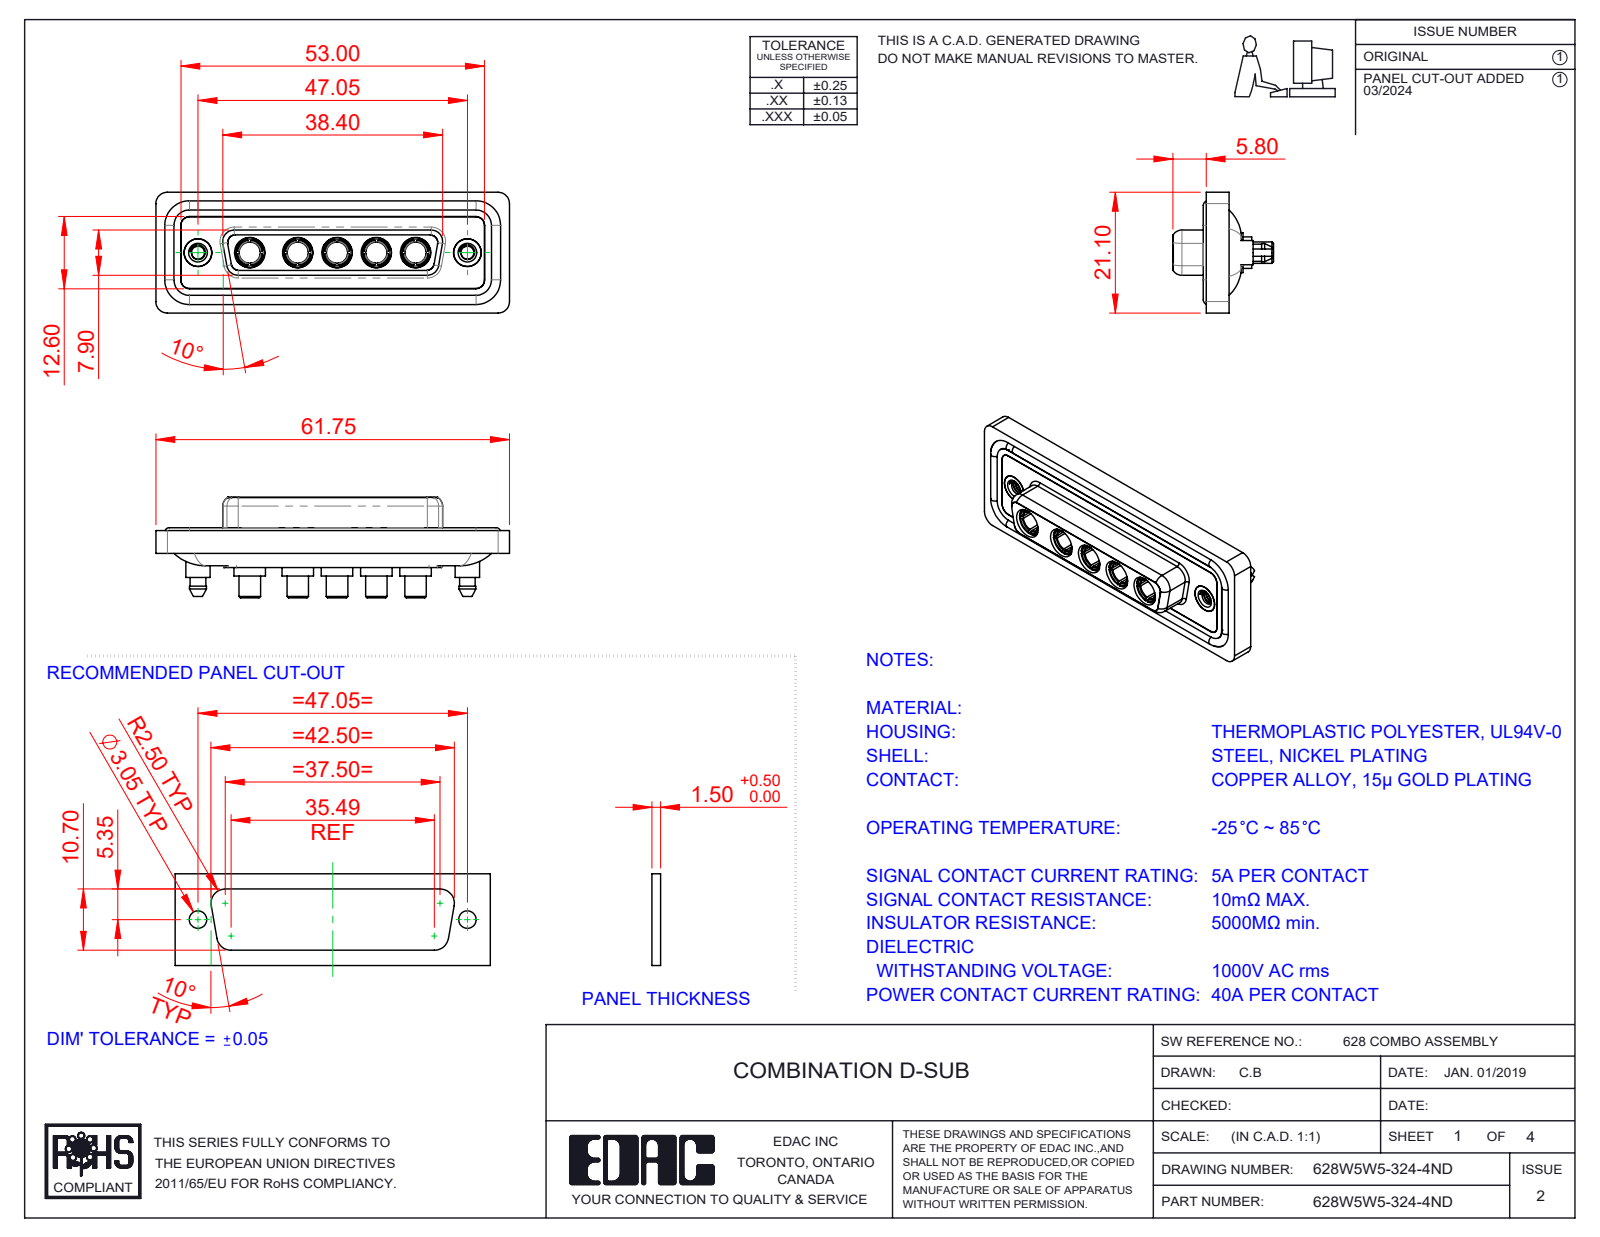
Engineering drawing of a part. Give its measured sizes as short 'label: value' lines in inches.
name: 628Combo Threaded Boardlock_D; 628Combo Housing_5W5; 628Combo Waterproof Housing_25 Contacts; 628Combo Shell Front_25 Contacts (+3 more)
written by: SolidWorks 2023 (CONFIG_CONTROL_DESIGN)
unit: in
bodies: 17 solids, 822 faces (266 planar, 351 cylindrical, 205 other)
size: 2.431 × 0.831 × 0.691
volume: 0.513 in³; area: 21.4 in²
holes: 7× ⌀0.191, 5× ⌀0.146, 5× ⌀0.209, 2× ⌀0.089, 2× ⌀0.157, 2× ⌀0.159, 2× ⌀0.197
bosses: 5× ⌀0.217, 5× ⌀0.205, 5× ⌀0.195, 5× ⌀0.187, 5× ⌀0.148, 4× ⌀0.063, 2× ⌀0.213, 2× ⌀0.195
rounds: 24× R0.059, 18× R0.079, 10× R0.063, 8× R0.053, 5× R0.083, 4× R0.01, 4× R0.02, 4× R0.024
face distances: 0.016, 0.071, 0.293, 0.222, 0.02, 0.278, 0.26, 0.063, 0.043, 0.114
hole spacings: 0.27, 0.356, 0.54, 1.496, 0.33, 0.6, 0.626, 0.686
